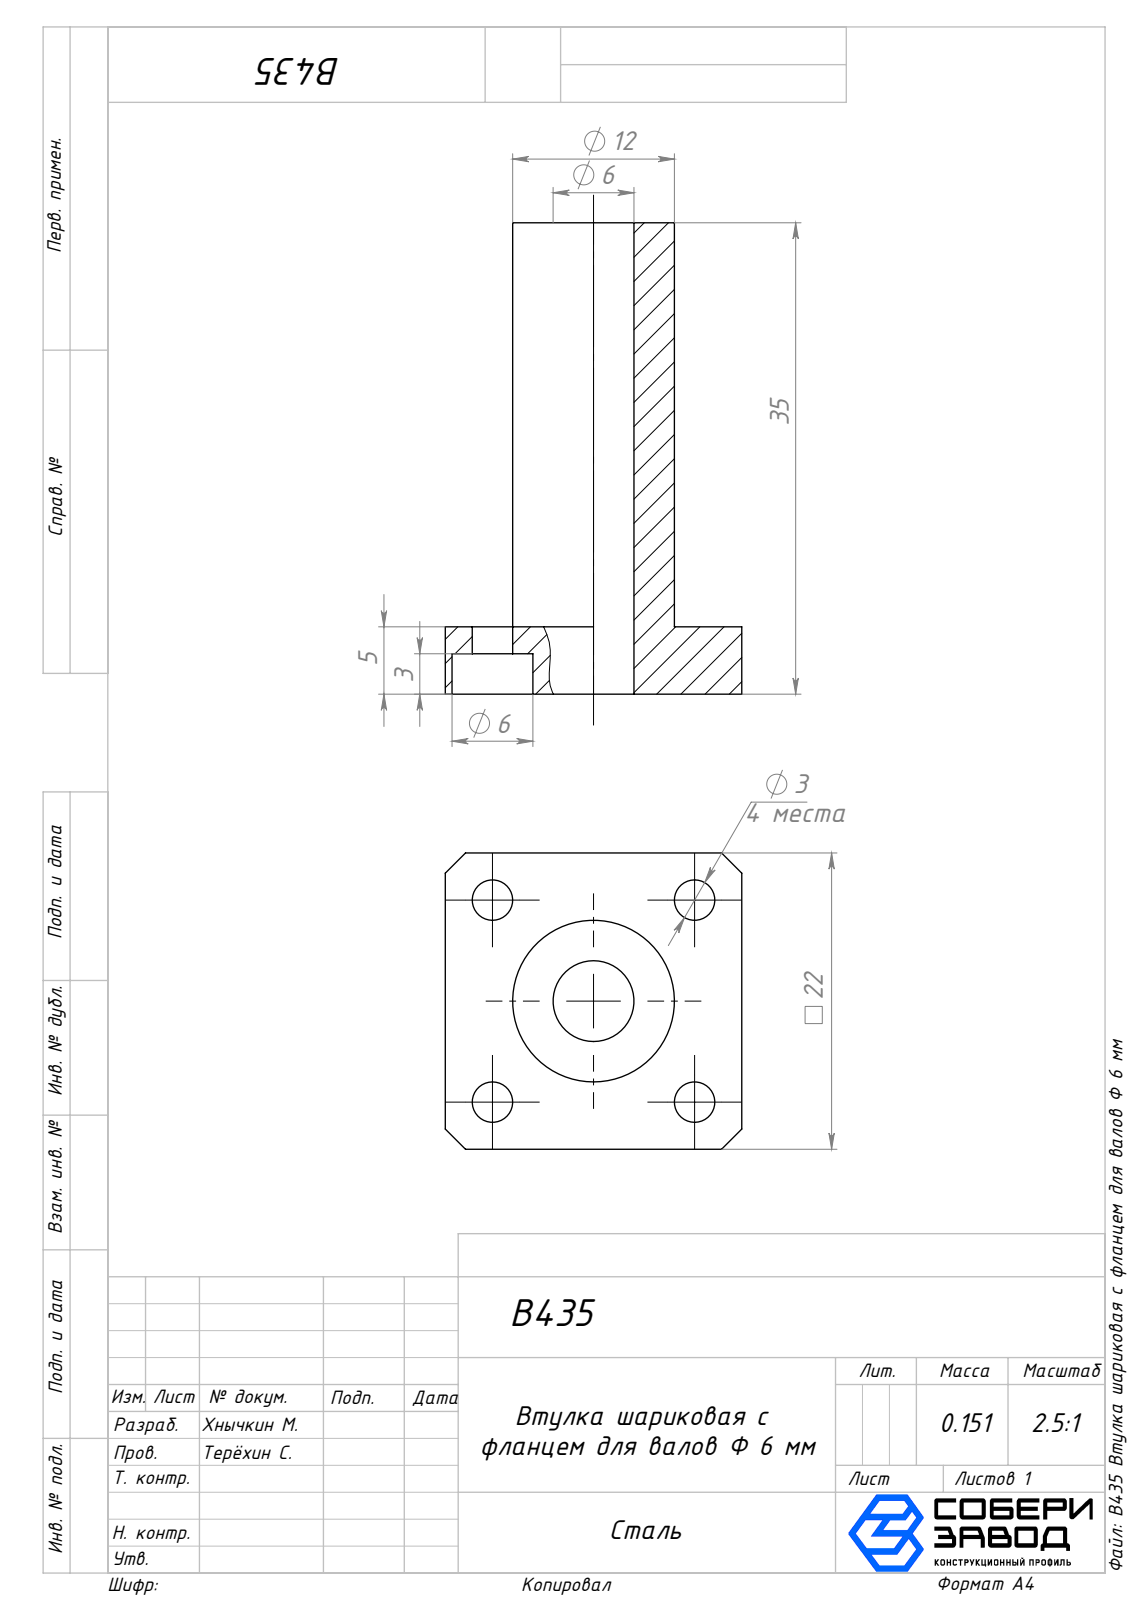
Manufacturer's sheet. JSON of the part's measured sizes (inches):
{"part_name": "B435 Втулка шариковая с фланцем для валов Ф 6 мм", "step_written_by": "SolidWorks 2025 (AUTOMOTIVE_DESIGN)", "units": "inches", "bodies": {"solids": 1, "faces": 35, "planar": 15, "cylindrical": 20, "other": 0}, "overall_size": [1.378, 0.866, 0.866], "volume_in3": 0.269, "surface_area_in2": 5.21, "round_holes": [[0.236, 5], [0.118, 4]], "round_bosses_or_shafts": [[0.472, 1]], "face_to_face_distances": [0.197, 0.866, 1.378, 1.181, 0.118, 0.079, 1.26, 1.141], "hole_center_spacings": [0.418, 0.591, 0.835]}
